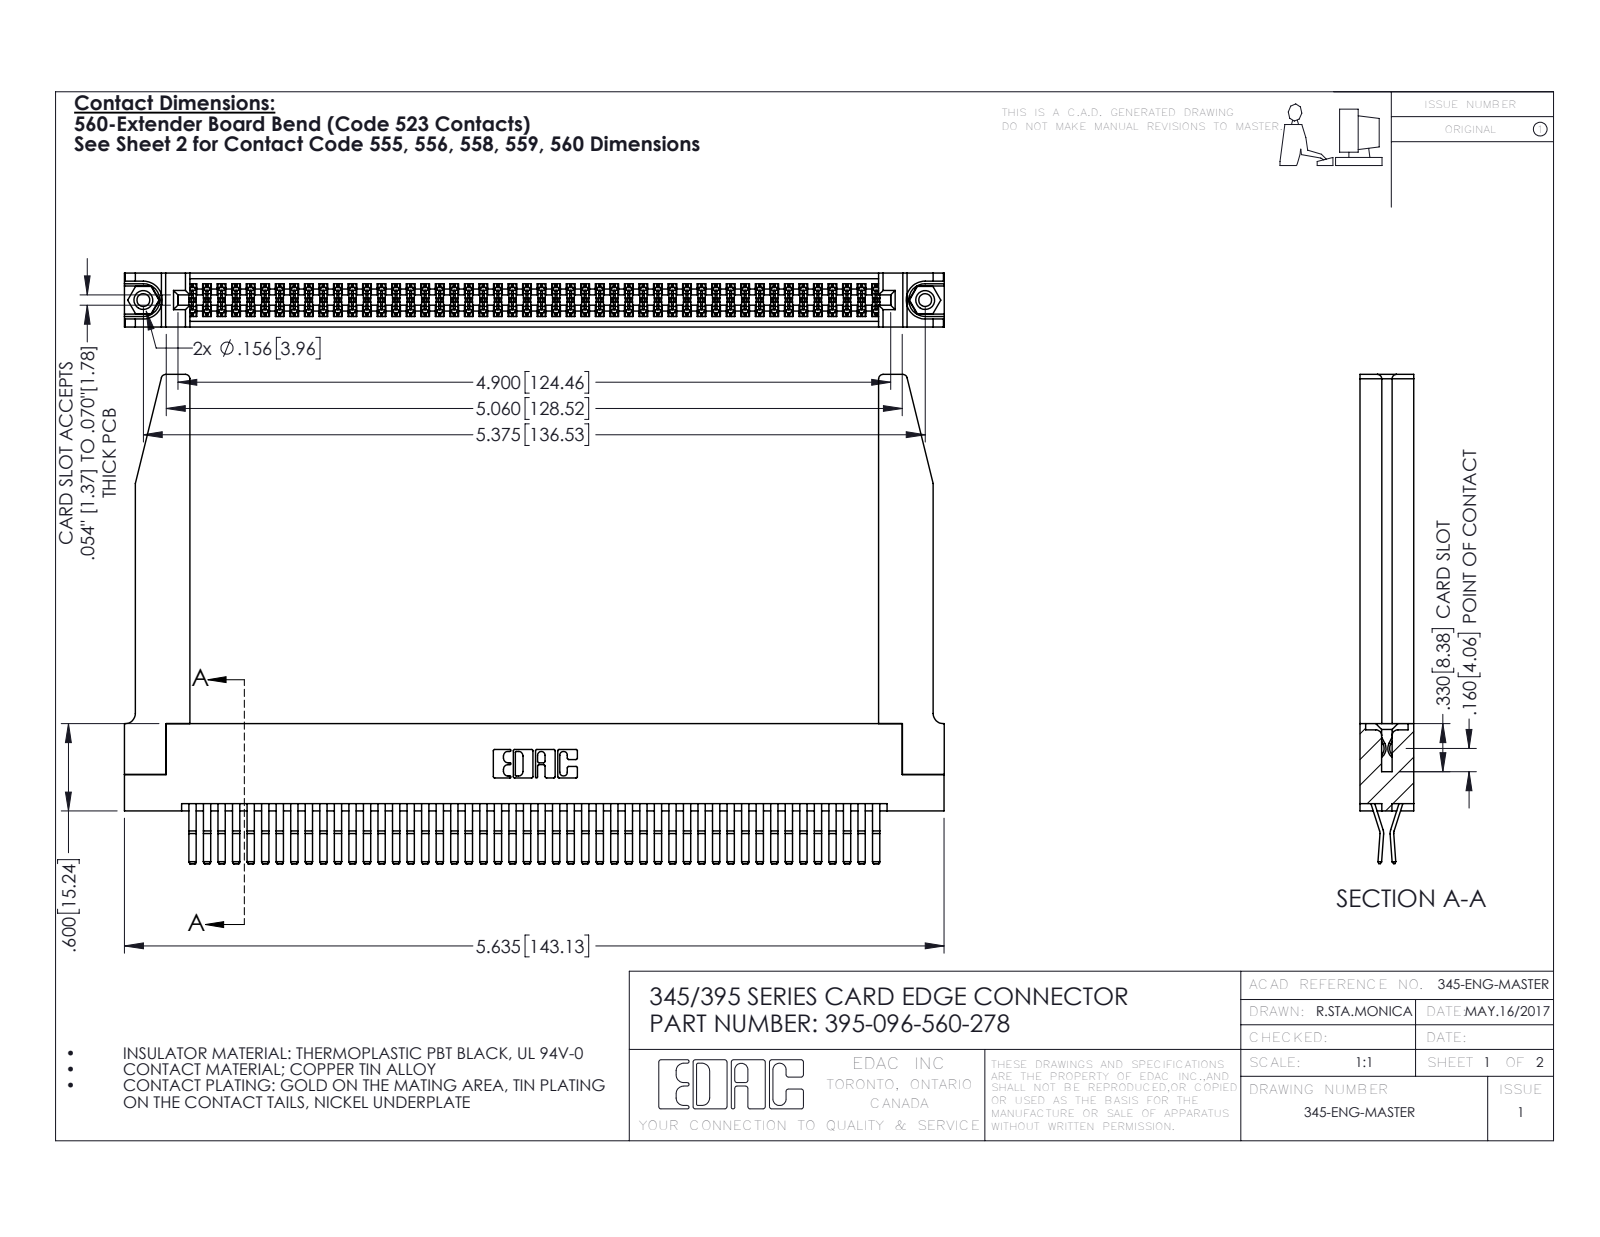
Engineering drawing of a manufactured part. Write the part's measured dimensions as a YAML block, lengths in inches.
part_name: "395-096-560-278; 345-292-001_560 Tail; 345 Part_Flush Mounting Lugs - 0.156 Dia-TH; 345-250-001_345-250-001-102 (+1 more)"
step_written_by: "SolidWorks 2016 (CONFIG_CONTROL_DESIGN)"
units: inches
bodies: {solids: 101, faces: 5352, planar: 3390, cylindrical: 1910, other: 52}
overall_size: [5.636, 3.362, 0.37]
volume: 1.365
surface_area: 46.72
round_holes:
  - {diameter: 0.089, count: 2}
  - {diameter: 0.125, count: 2}
  - {diameter: 0.156, count: 2}
  - {diameter: 0.064, count: 1}
round_bosses_or_shafts:
  - {diameter: 0.155, count: 2}
partial_cylinders:
  - {radius: 0.006, count: 144}
  - {radius: 0.01, count: 22}
  - {radius: 0.03, count: 8}
  - {radius: 0.007, count: 6}
  - {radius: 0.031, count: 6}
  - {radius: 0.026, count: 3}
  - {radius: 0.01, count: 2}
  - {radius: 0.014, count: 2}
face_to_face_distances: [0.072, 0.37, 0.298, 0.025, 0.2, 0.098, 0.272, 0.225, 0.15, 0.148]
hole_center_spacings: [0.27, 5.139, 5.375]
